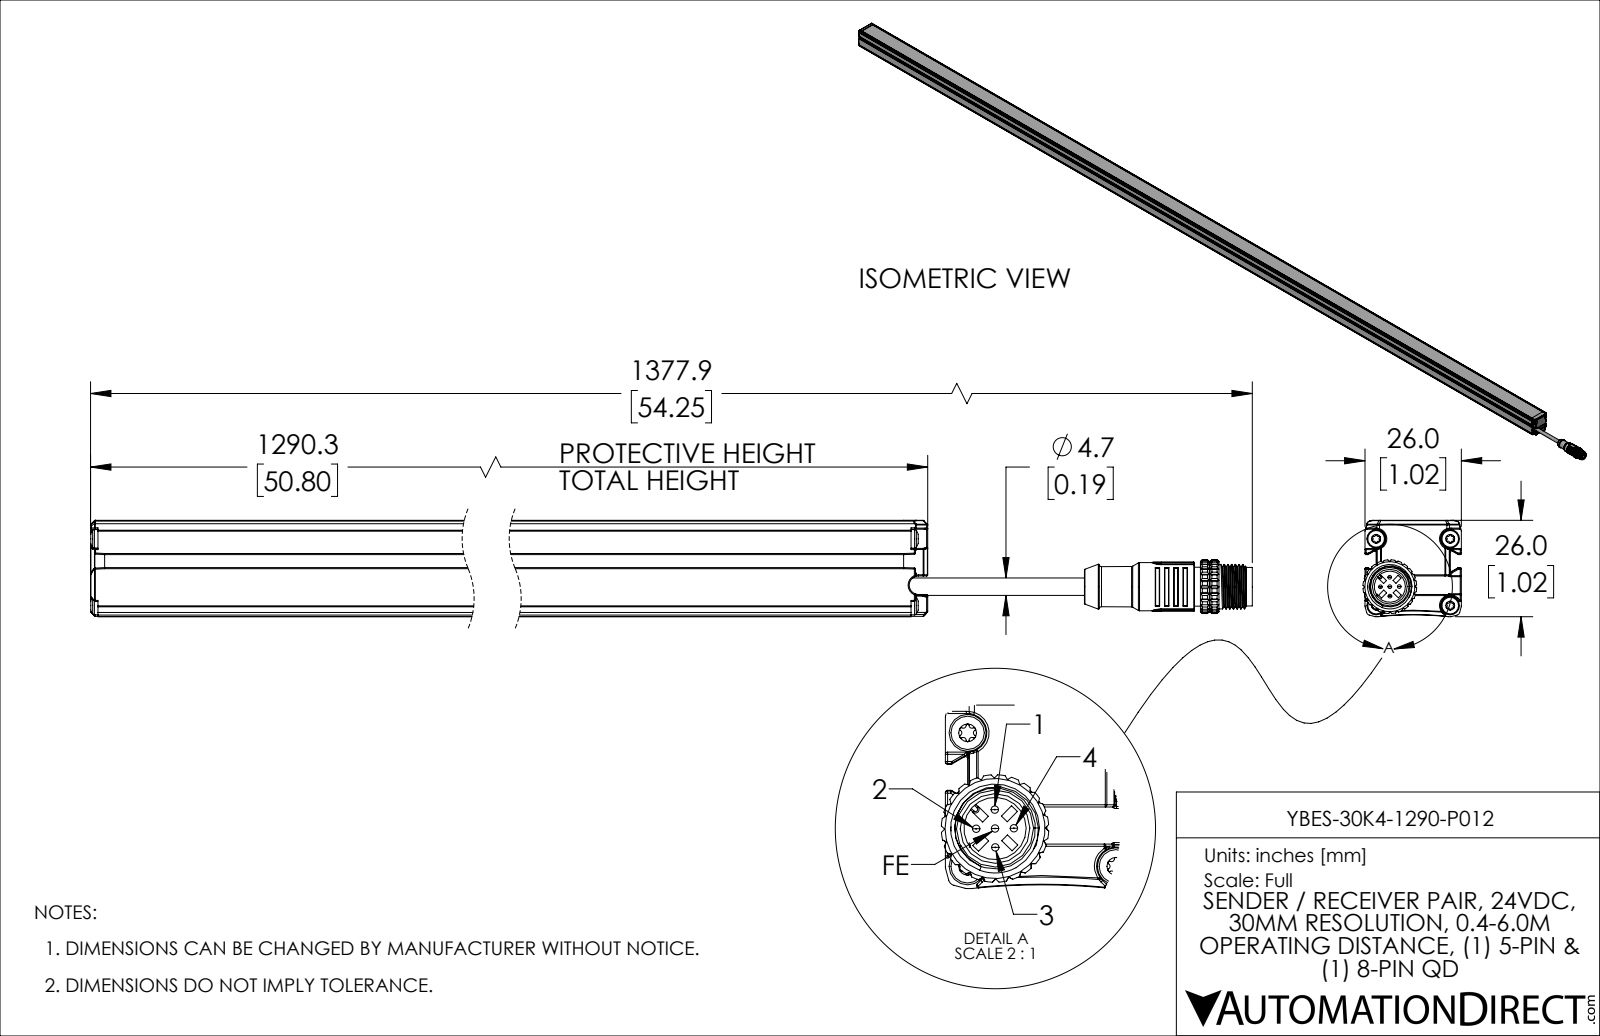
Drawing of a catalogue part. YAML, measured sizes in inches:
part_name: "YBES-30K4-1290-P012_REV1"
step_written_by: "SolidWorks 2019 (AUTOMOTIVE_DESIGN)"
units: inches
bodies: {solids: 2, faces: 1743, planar: 549, cylindrical: 719, other: 475}
overall_size: [54.248, 1.045, 1.024]
volume: 18.31
surface_area: 508.2
round_holes:
  - {diameter: 0.094, count: 4}
  - {diameter: 0.1, count: 4}
  - {diameter: 0.146, count: 4}
  - {diameter: 0.197, count: 4}
  - {diameter: 0.189, count: 1}
  - {diameter: 0.232, count: 1}
  - {diameter: 0.331, count: 1}
round_bosses_or_shafts:
  - {diameter: 0.039, count: 5}
  - {diameter: 0.126, count: 4}
  - {diameter: 0.098, count: 4}
  - {diameter: 0.051, count: 4}
  - {diameter: 0.059, count: 2}
  - {diameter: 0.531, count: 1}
  - {diameter: 0.512, count: 1}
  - {diameter: 0.472, count: 1}
partial_cylinders:
  - {radius: 0.008, count: 153}
  - {radius: 0.012, count: 115}
  - {radius: 0.008, count: 24}
  - {radius: 0.015, count: 24}
  - {radius: 0.039, count: 18}
  - {radius: 0.016, count: 16}
  - {radius: 0.006, count: 10}
  - {radius: 0.02, count: 7}
face_to_face_distances: [0.118, 0.059, 0.071, 0.835, 1.024, 0.717, 0.047, 0.016, 0.906, 0.189]
hole_center_spacings: [0.709, 0.787, 1.059, 0.248, 0.528, 0.672, 0.819]
